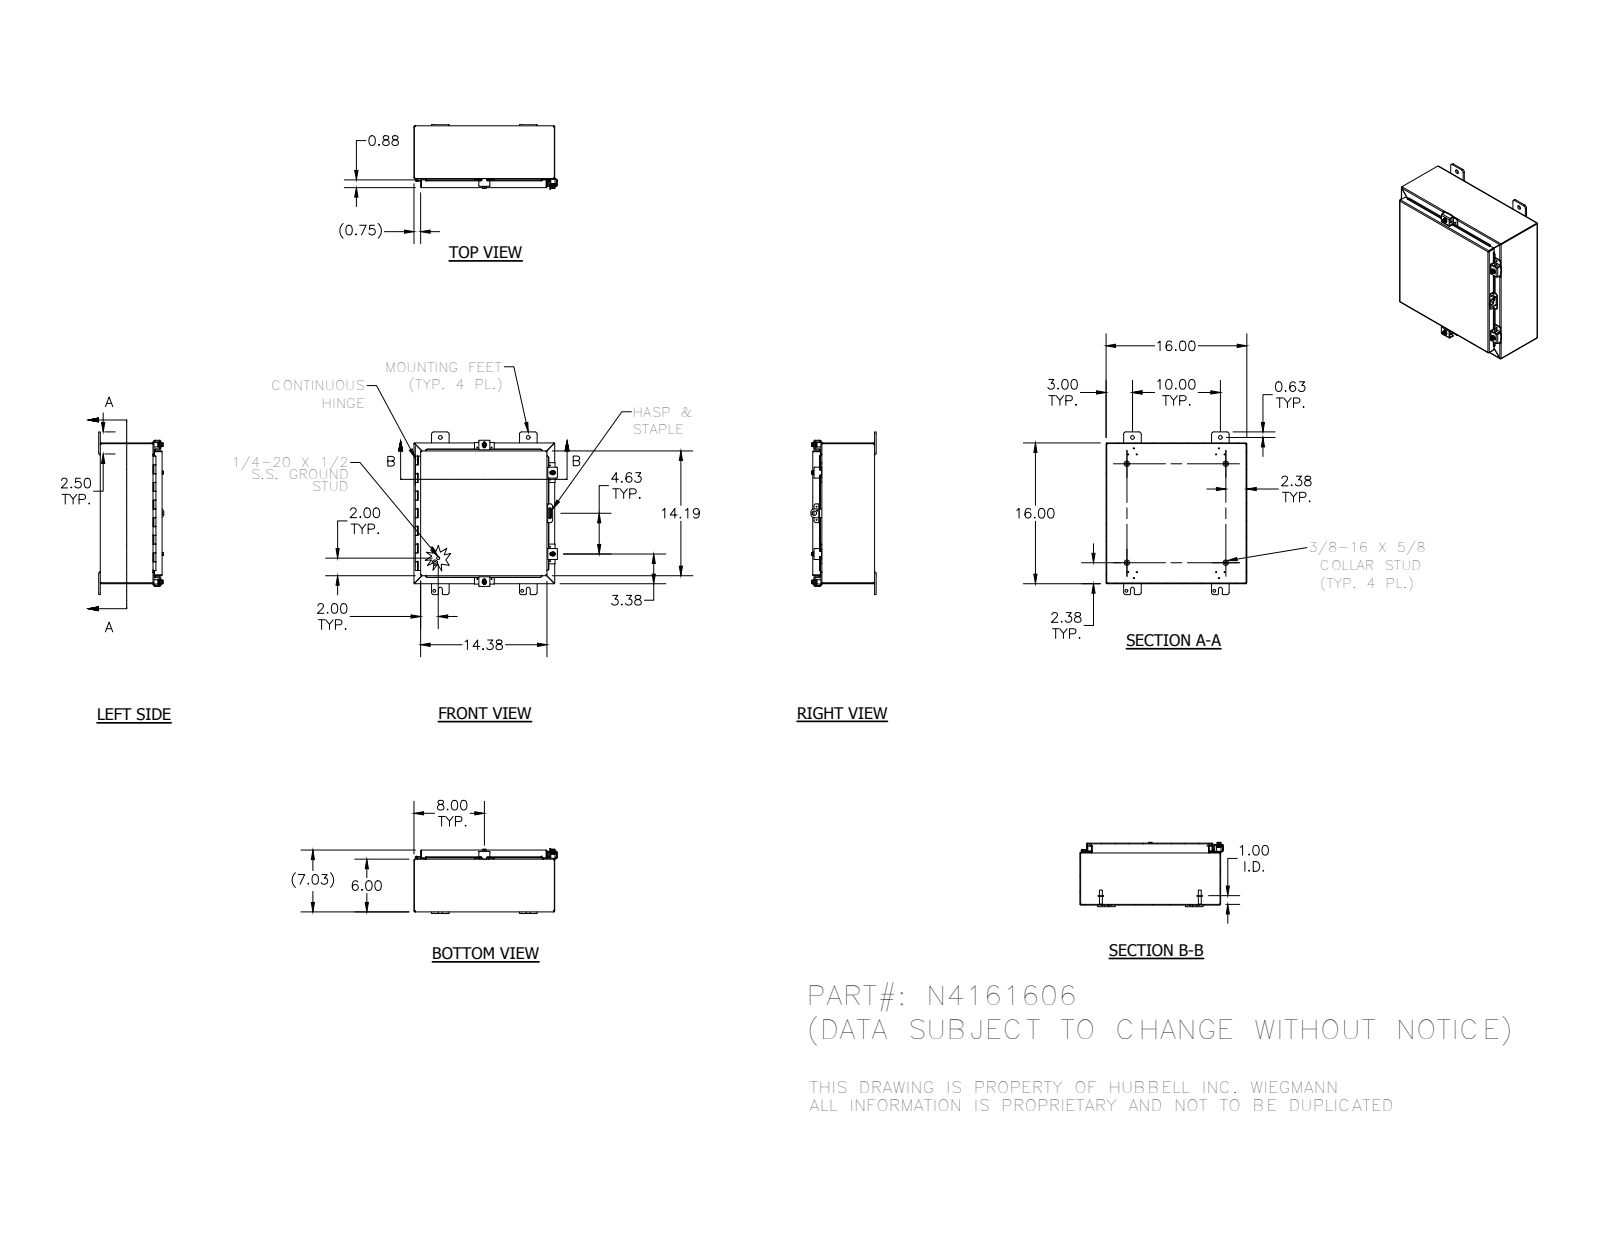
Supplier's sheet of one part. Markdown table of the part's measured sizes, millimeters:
| quantity | value |
| --- | --- |
| part name | 388116_1; 34840_1; 328103P-1_1; 30824_1 (+8 more) |
| STEP written by | SolidWorks 2014 (AUTOMOTIVE_DESIGN) |
| units | millimeters |
| bodies | 37 solids, 1568 faces (611 planar, 700 cylindrical, 257 other) |
| overall size | 469.9 × 414.3 × 188.2 |
| volume | 1 460 000 mm³ |
| surface area | 1 477 000 mm² |
| round holes (diameter × count) | 3 × 12, 2.8 × 11, 5.4 × 4, 7.1 × 4, 7.6 × 4, 8 × 4, 11.1 × 4, 3.2 × 1, 4 × 1, 12.7 × 1 |
| round bosses / shafts (diameter × count) | 6.4 × 6, 15.9 × 4, 13.2 × 4, 12.7 × 4, 8.9 × 4, 8.4 × 4, 2.9 × 2, 8.6 × 1 |
| partial cylindrical surfaces (radius × count) | 0.8 × 49, 3.2 × 33, 1.6 × 29, 6.4 × 29, 0.8 × 23, 2.7 × 23, 1.6 × 10, 1.8 × 8 |
| main face-to-face distances | 1.9, 176.8, 404.5, 174.9, 178.6, 406.4, 402.6, 150.5, 26.2, 152.4 |
| hole center spacings | 254, 22.3, 19.3, 23.9, 24.6, 50.7, 96.2, 102.4 |
